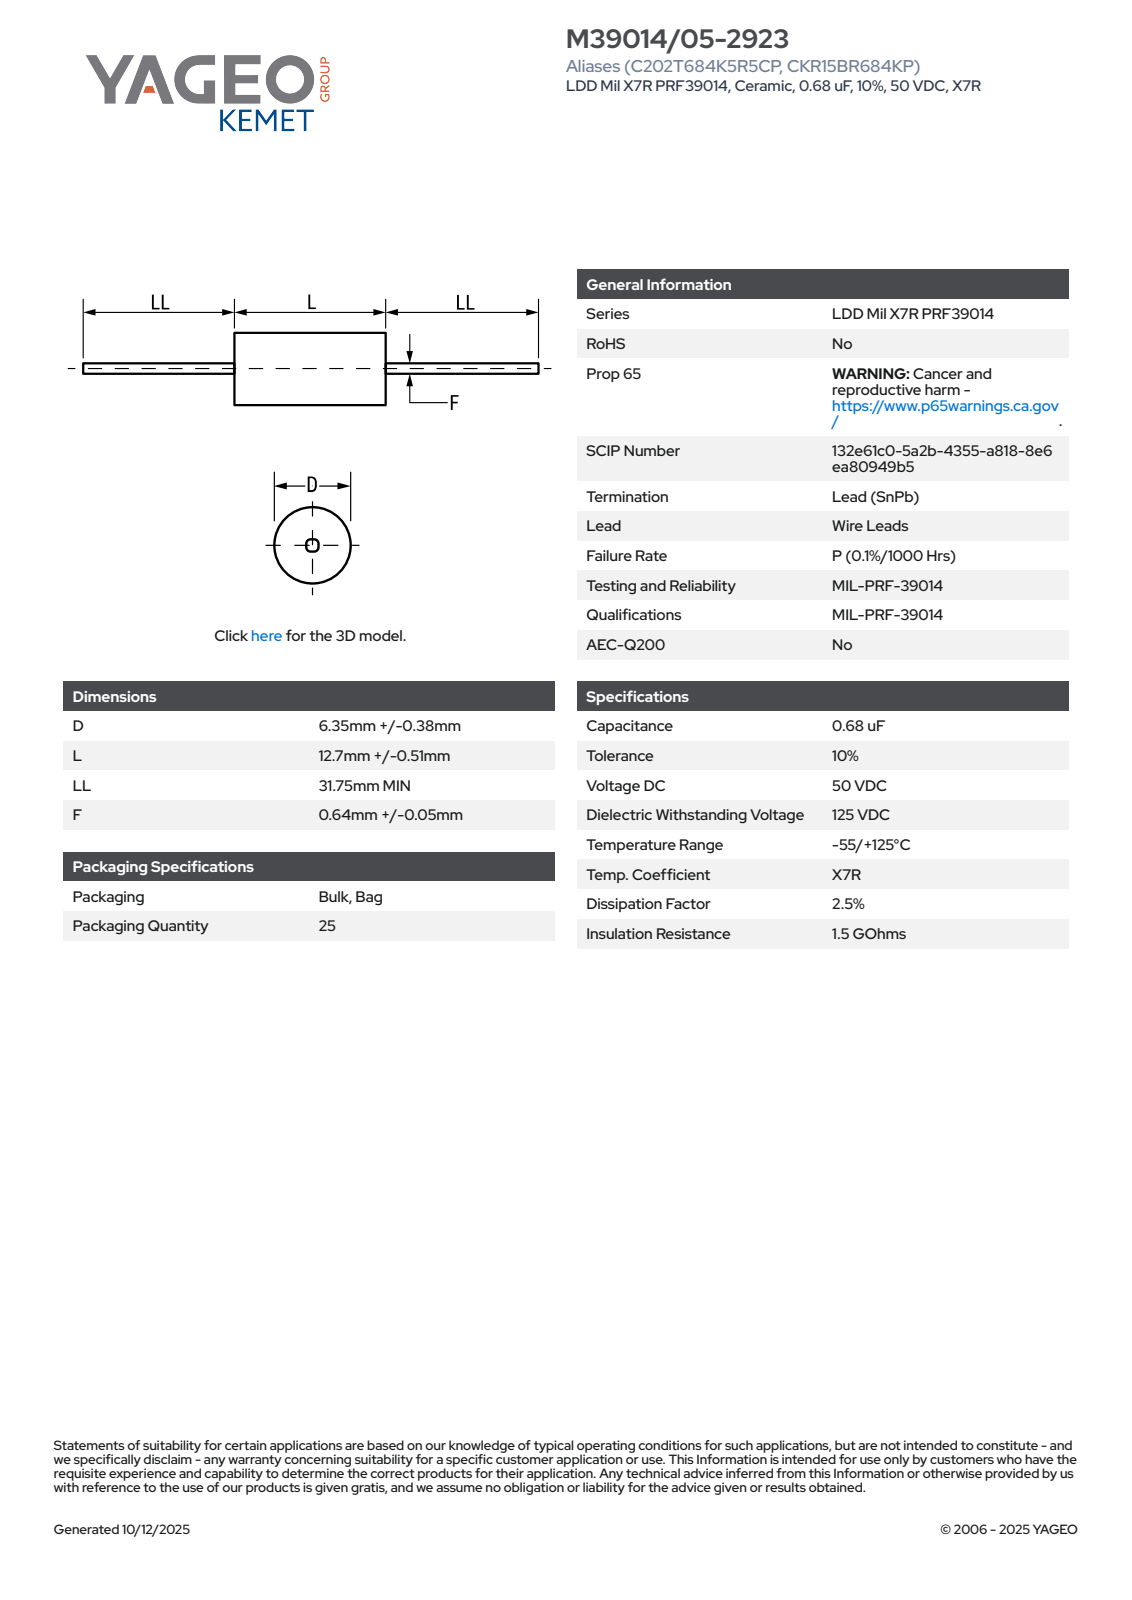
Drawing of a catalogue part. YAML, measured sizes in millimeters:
part_name: "CCA_AXM_C202_D6.73L13.21LL38.1F0.69"
step_written_by: "SolidWorks 2014 (AUTOMOTIVE_DESIGN)"
units: millimeters
bodies: {solids: 1, faces: 66, planar: 26, cylindrical: 9, other: 31}
overall_size: [89.41, 6.73, 6.73]
volume: 498
surface_area: 516
round_bosses_or_shafts:
  - {diameter: 6.73, count: 1}
  - {diameter: 0.69, count: 1}
partial_cylinders:
  - {radius: 3.35, count: 1}
face_to_face_distances: [13.2, 38.1, 51.3, 89.4]
